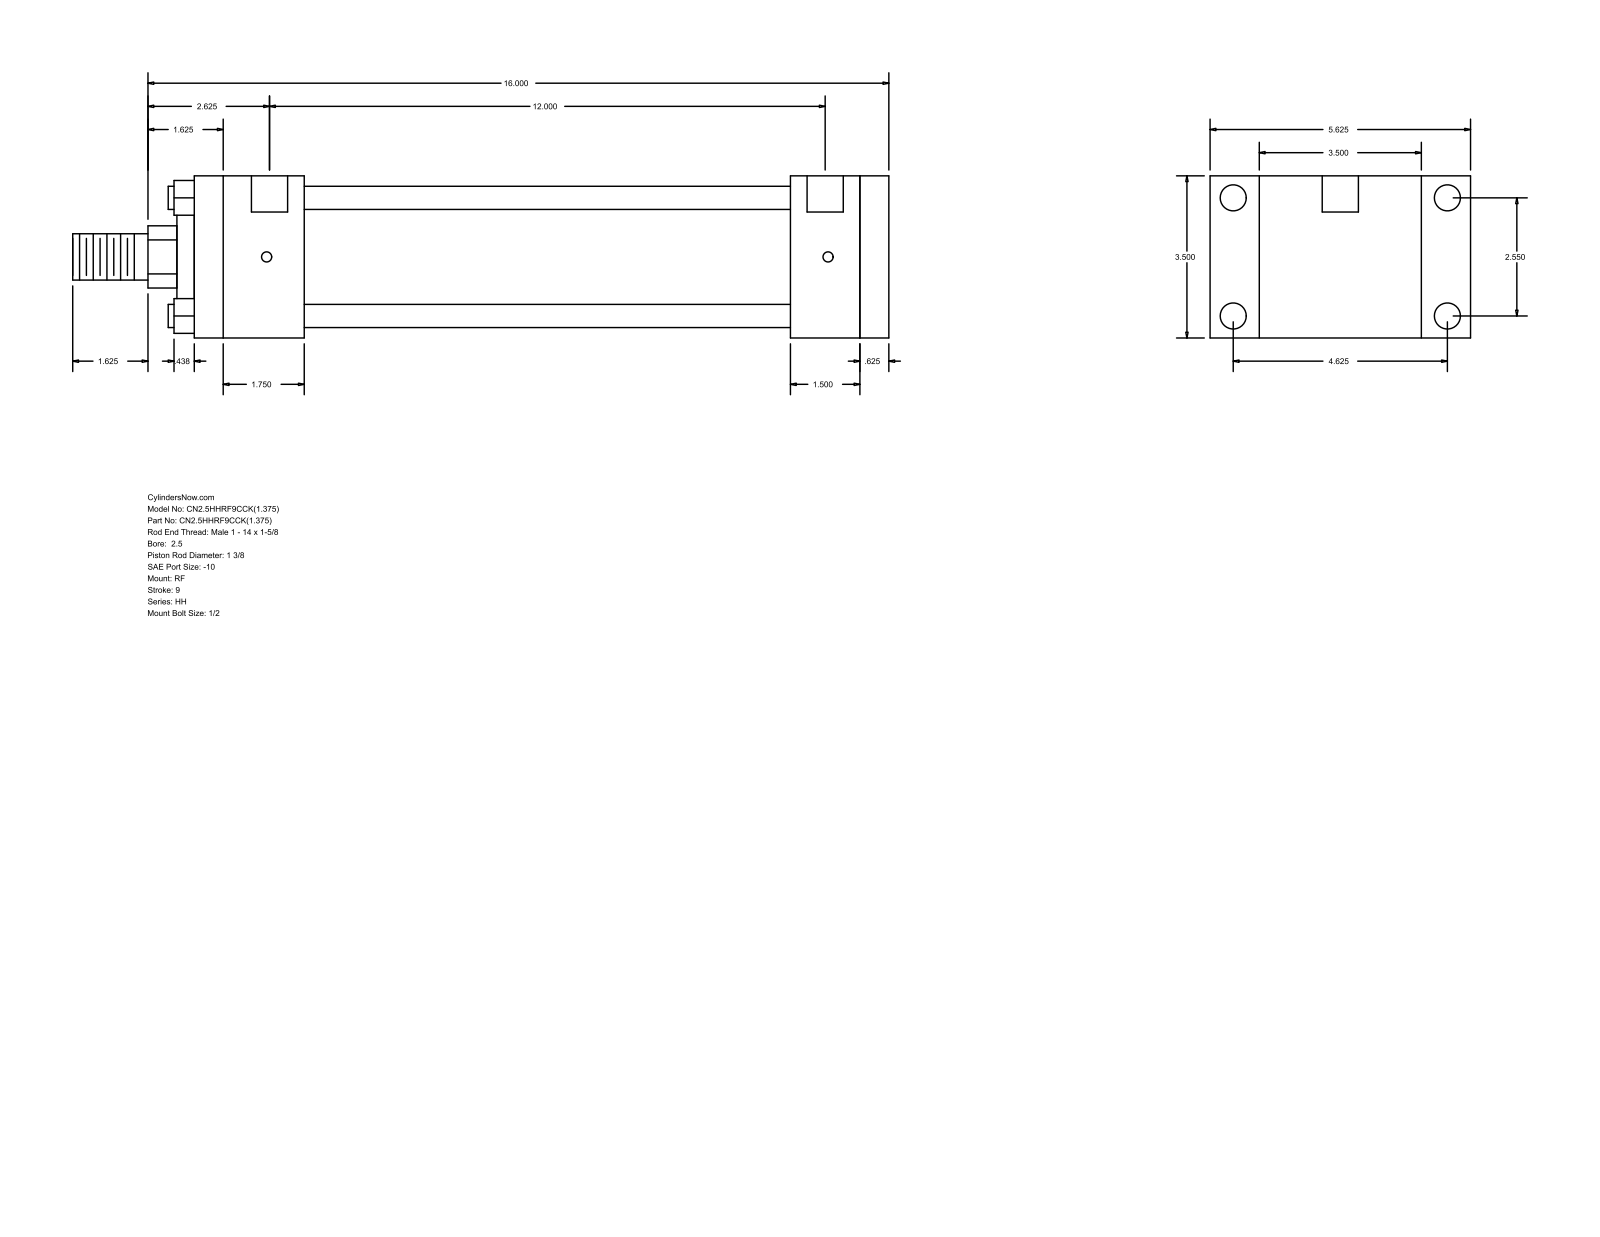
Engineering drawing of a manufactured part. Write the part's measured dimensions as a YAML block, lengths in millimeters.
part_name: "HH_RF__0250_1.375"
step_written_by: "GSSL Pune (CONFIG_CONTROL_DESIGN)"
units: millimeters
bodies: {solids: 0, faces: 92, planar: 64, cylindrical: 28, other: 0}
overall_size: [447.68, 142.88, 88.9]
round_holes:
  - {diameter: 5.56, count: 4}
  - {diameter: 14.3, count: 4}
  - {diameter: 19.84, count: 2}
round_bosses_or_shafts:
  - {diameter: 12.7, count: 4}
  - {diameter: 73.03, count: 1}
  - {diameter: 50.8, count: 1}
  - {diameter: 34.92, count: 1}
  - {diameter: 25.4, count: 1}
partial_cylinders:
  - {radius: 17.06, count: 1}
face_to_face_distances: [88.9, 381, 15.88, 365.12, 53.97, 60.32, 304.8, 320.68, 327.03, 266.71]
hole_center_spacings: [1.58, 64.76, 117.48, 134.15, 306.39, 307.97, 304.81]
